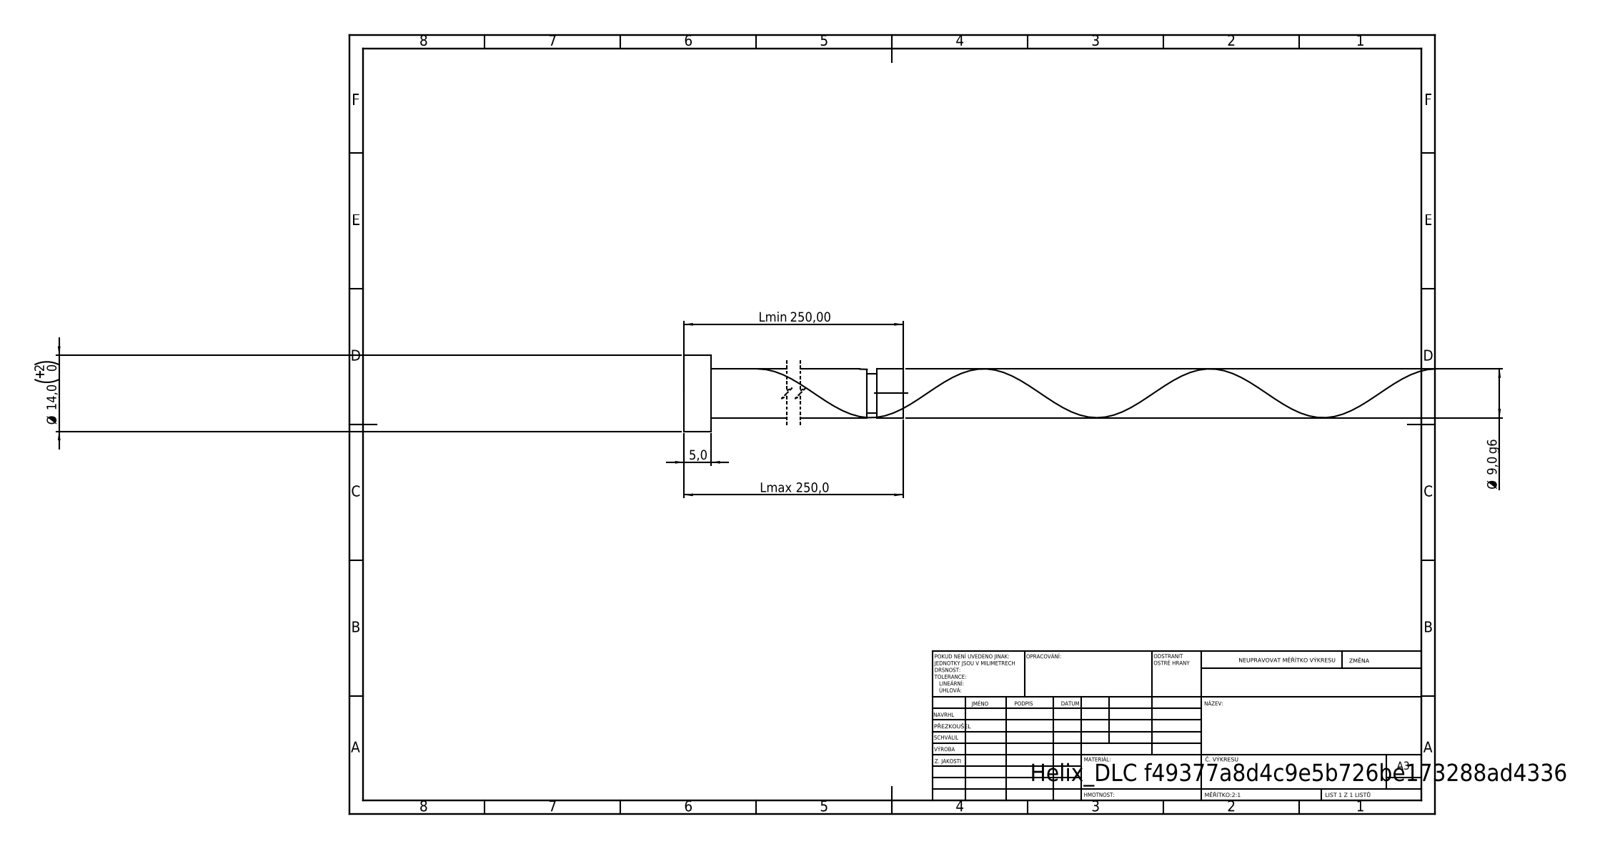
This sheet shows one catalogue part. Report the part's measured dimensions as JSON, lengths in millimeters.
{"step_written_by": "SolidWorks 2019 (CONFIG_CONTROL_DESIGN)", "units": "millimeters", "bodies": {"solids": 1, "faces": 21, "planar": 6, "cylindrical": 14, "other": 1}, "overall_size": [250, 14, 14], "volume_mm3": 16162, "surface_area_mm2": 7629, "round_bosses_or_shafts": [[14, 1], [9, 1], [7.2, 1]], "face_to_face_distances": [5, 250, 245, 245.16, 240.16, 4.84, 243.36, 238.36, 1.8, 6.64]}
